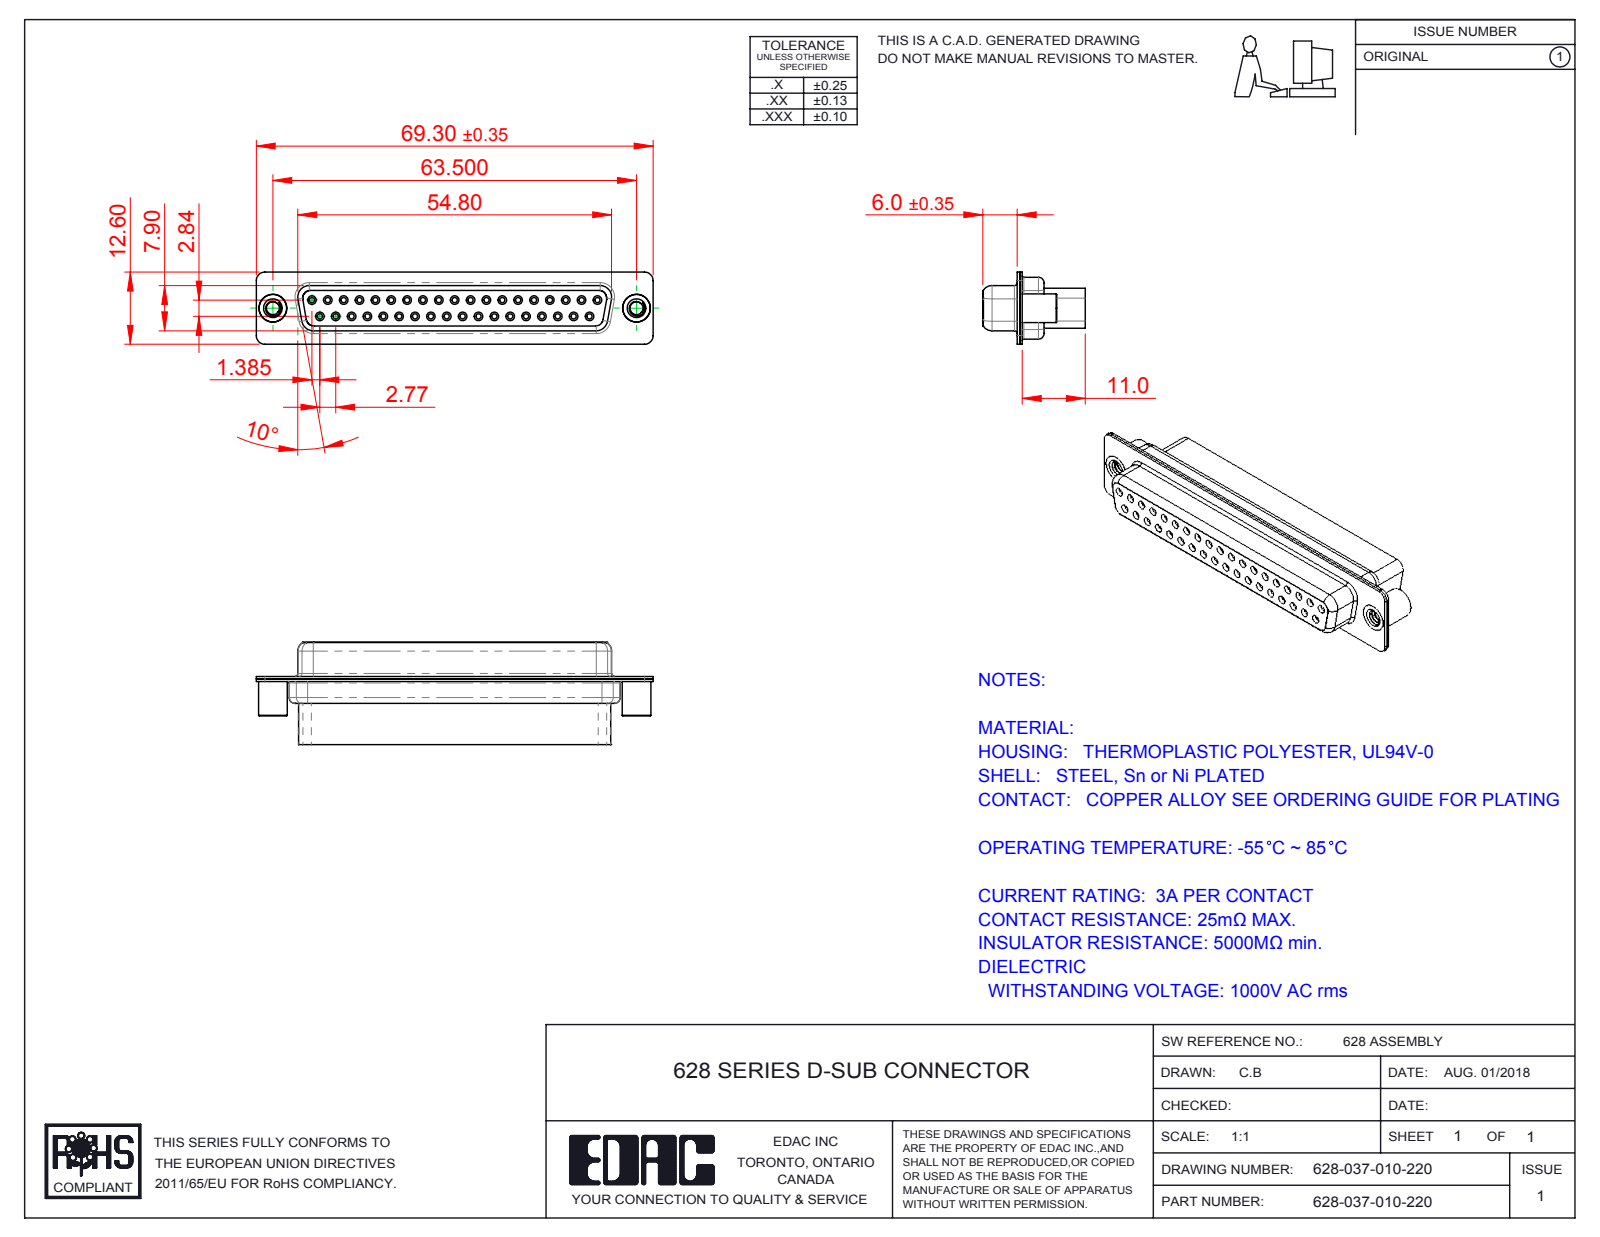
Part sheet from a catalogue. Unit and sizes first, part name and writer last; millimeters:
Units: millimetres
Overall size (bounding box): 69.3 × 17.9 × 12.6
Round holes (diameter × count): ⌀0.9 ×37, ⌀1.5 ×37, ⌀2 ×37, ⌀1.7 ×19, ⌀1.6 ×18, ⌀2.26 ×2, ⌀4 ×2, ⌀4.05 ×2, ⌀4.85 ×2
Round bosses / shafts (diameter × count): ⌀5 ×2, ⌀4.95 ×2, ⌀4.8 ×2
Partial cylindrical surfaces — rounded edges, fillets, slot ends (radius × count): R1.5 ×16, R2 ×12, R0.25 ×4, R0.5 ×4, R0.6 ×4, R0.65 ×4, R0.95 ×4, R1 ×4
Main face-to-face distances: 0.4, 0.45, 6.6, 7, 1.9, 8.5, 0.85, 7.05, 7.45, 1.4
Hole centre spacings: 3.16, 2.77, 5.54, 8.31, 5.04, 7.49, 11.08, 13.85
Volume: 6 761 mm³ · Surface area: 11 144 mm²
Bodies: 5 solids, 782 faces (178 planar, 453 cylindrical, 151 other)
Part name (STEP PRODUCT): 628 4-40 Threaded Standoff BS; 628 Housing_37 HP; 628-050-010-220; 628 Shell Front_37 Contacts (+1 more)
STEP written by: SolidWorks 2016 (CONFIG_CONTROL_DESIGN)
